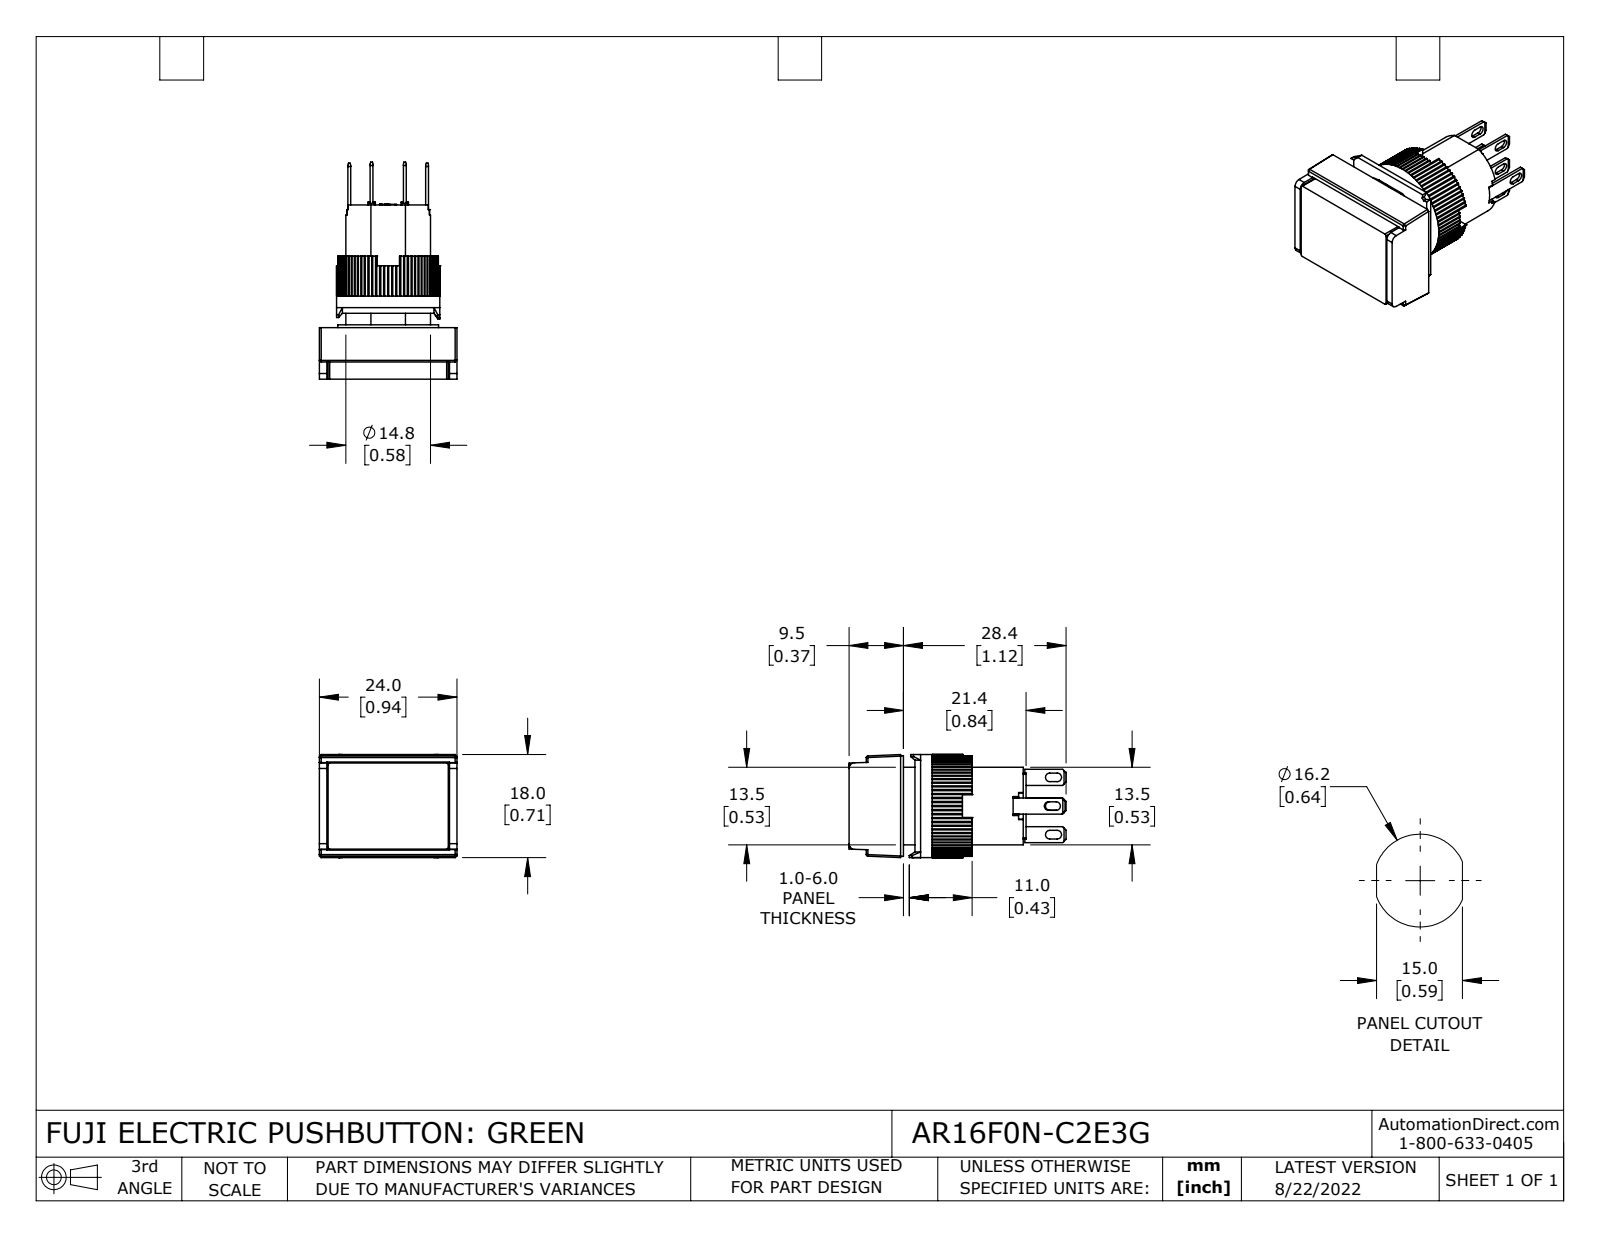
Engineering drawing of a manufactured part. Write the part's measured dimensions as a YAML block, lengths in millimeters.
part_name: "AR16F0N-C2E3G"
step_written_by: "SolidWorks 2021 (CONFIG_CONTROL_DESIGN)"
units: millimeters
bodies: {solids: 14, faces: 843, planar: 656, cylindrical: 183, other: 4}
overall_size: [37.9, 24, 18]
volume: 7280
surface_area: 6004
round_holes:
  - {diameter: 13.8, count: 1}
  - {diameter: 14.8, count: 1}
round_bosses_or_shafts:
  - {diameter: 18, count: 1}
  - {diameter: 17.6, count: 1}
partial_cylinders:
  - {radius: 0.3, count: 80}
  - {radius: 0.2, count: 12}
  - {radius: 0.8, count: 8}
  - {radius: 0.3, count: 6}
  - {radius: 1, count: 2}
face_to_face_distances: [5.4, 9, 3.6, 8.9, 12.5, 3.5, 0.5, 21.4, 1.5, 11.5]
